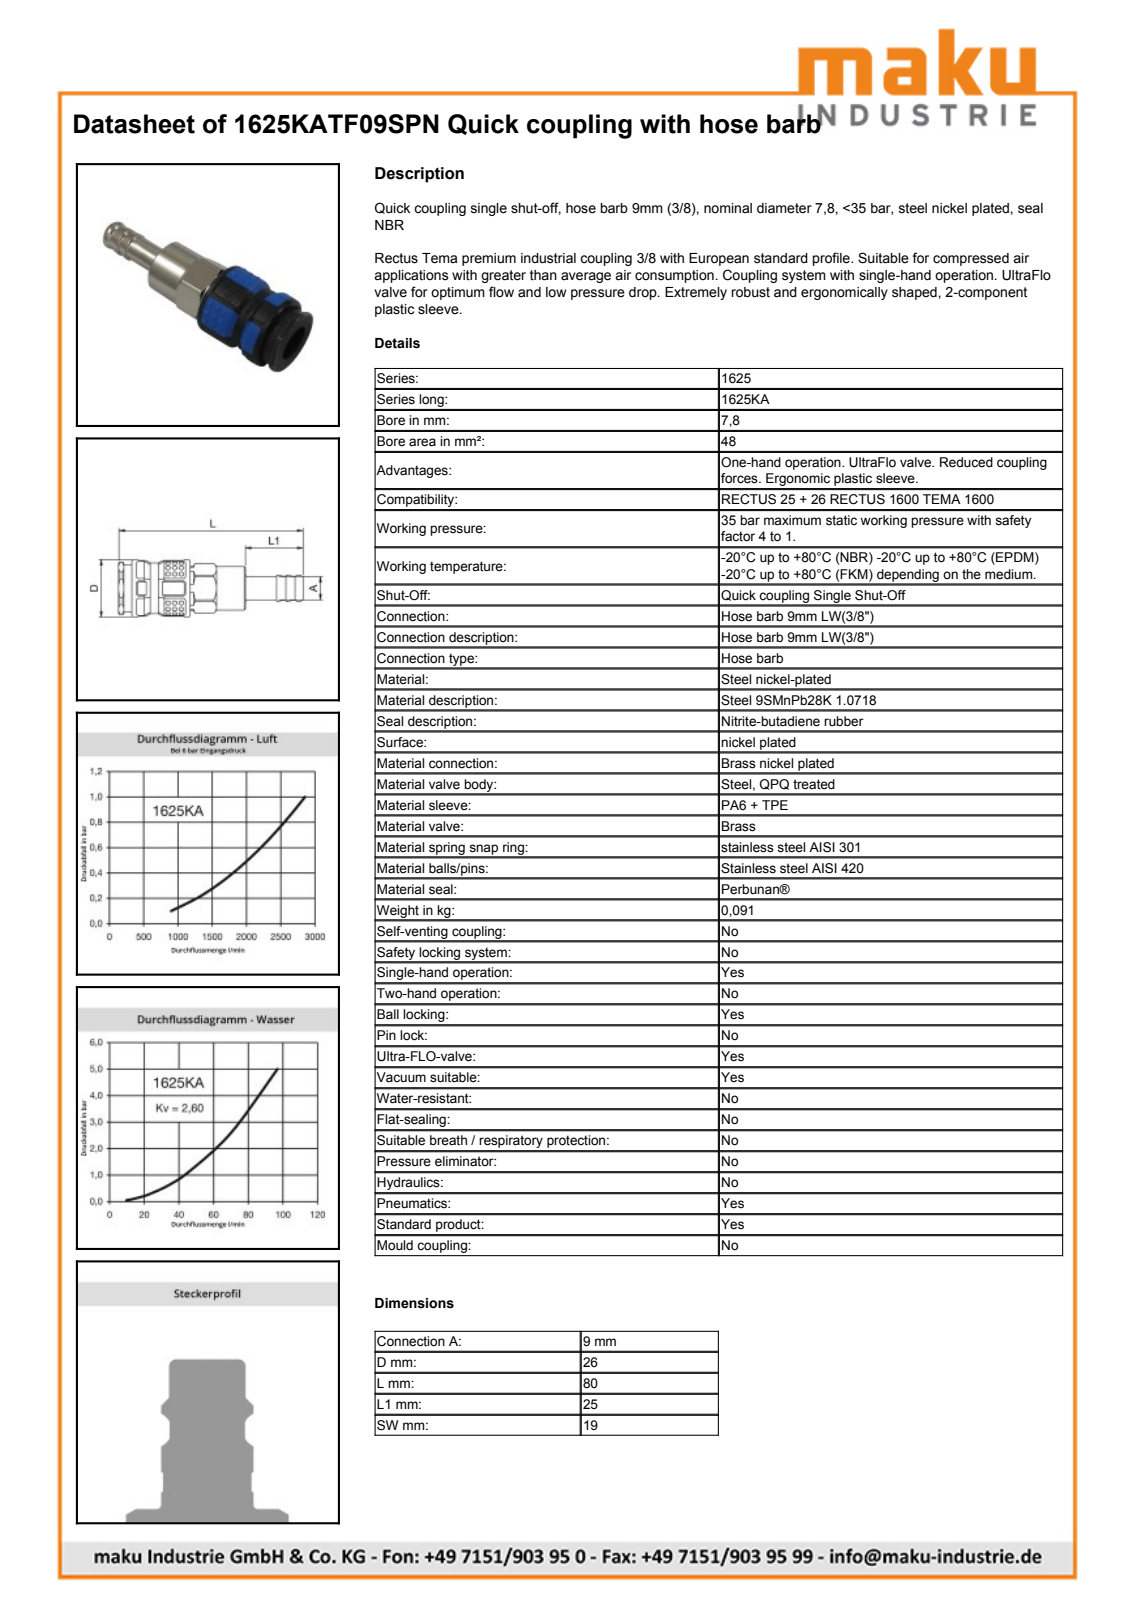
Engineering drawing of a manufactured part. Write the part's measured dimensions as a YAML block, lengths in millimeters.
part_name: "D105562"
step_written_by: "Autodesk Inventor 2011 (AUTOMOTIVE_DESIGN)"
units: millimeters
bodies: {solids: 2, faces: 976, planar: 355, cylindrical: 154, other: 467}
overall_size: [79.79, 25, 25]
volume: 20712
surface_area: 11903
round_holes:
  - {diameter: 1, count: 4}
  - {diameter: 14, count: 1}
  - {diameter: 14.5, count: 1}
  - {diameter: 16.15, count: 1}
  - {diameter: 17.2, count: 1}
  - {diameter: 17.9, count: 1}
  - {diameter: 19.6, count: 1}
  - {diameter: 20.7, count: 1}
round_bosses_or_shafts:
  - {diameter: 25, count: 1}
  - {diameter: 22, count: 1}
  - {diameter: 20.3, count: 1}
  - {diameter: 18.8, count: 1}
  - {diameter: 17.6, count: 1}
  - {diameter: 17, count: 1}
  - {diameter: 15.7, count: 1}
  - {diameter: 14.45, count: 1}
partial_cylinders:
  - {radius: 0.4, count: 8}
  - {radius: 9.65, count: 1}
  - {radius: 10.7, count: 1}
  - {radius: 11.2, count: 1}
  - {radius: 11.25, count: 1}
  - {radius: 11.5, count: 1}
  - {radius: 12, count: 1}
  - {radius: 12.3, count: 1}
face_to_face_distances: [19, 54.79, 30.93, 23.86, 25.3, 5.63, 49.16, 79.79, 74.16, 48.86]
hole_center_spacings: [12.8]
